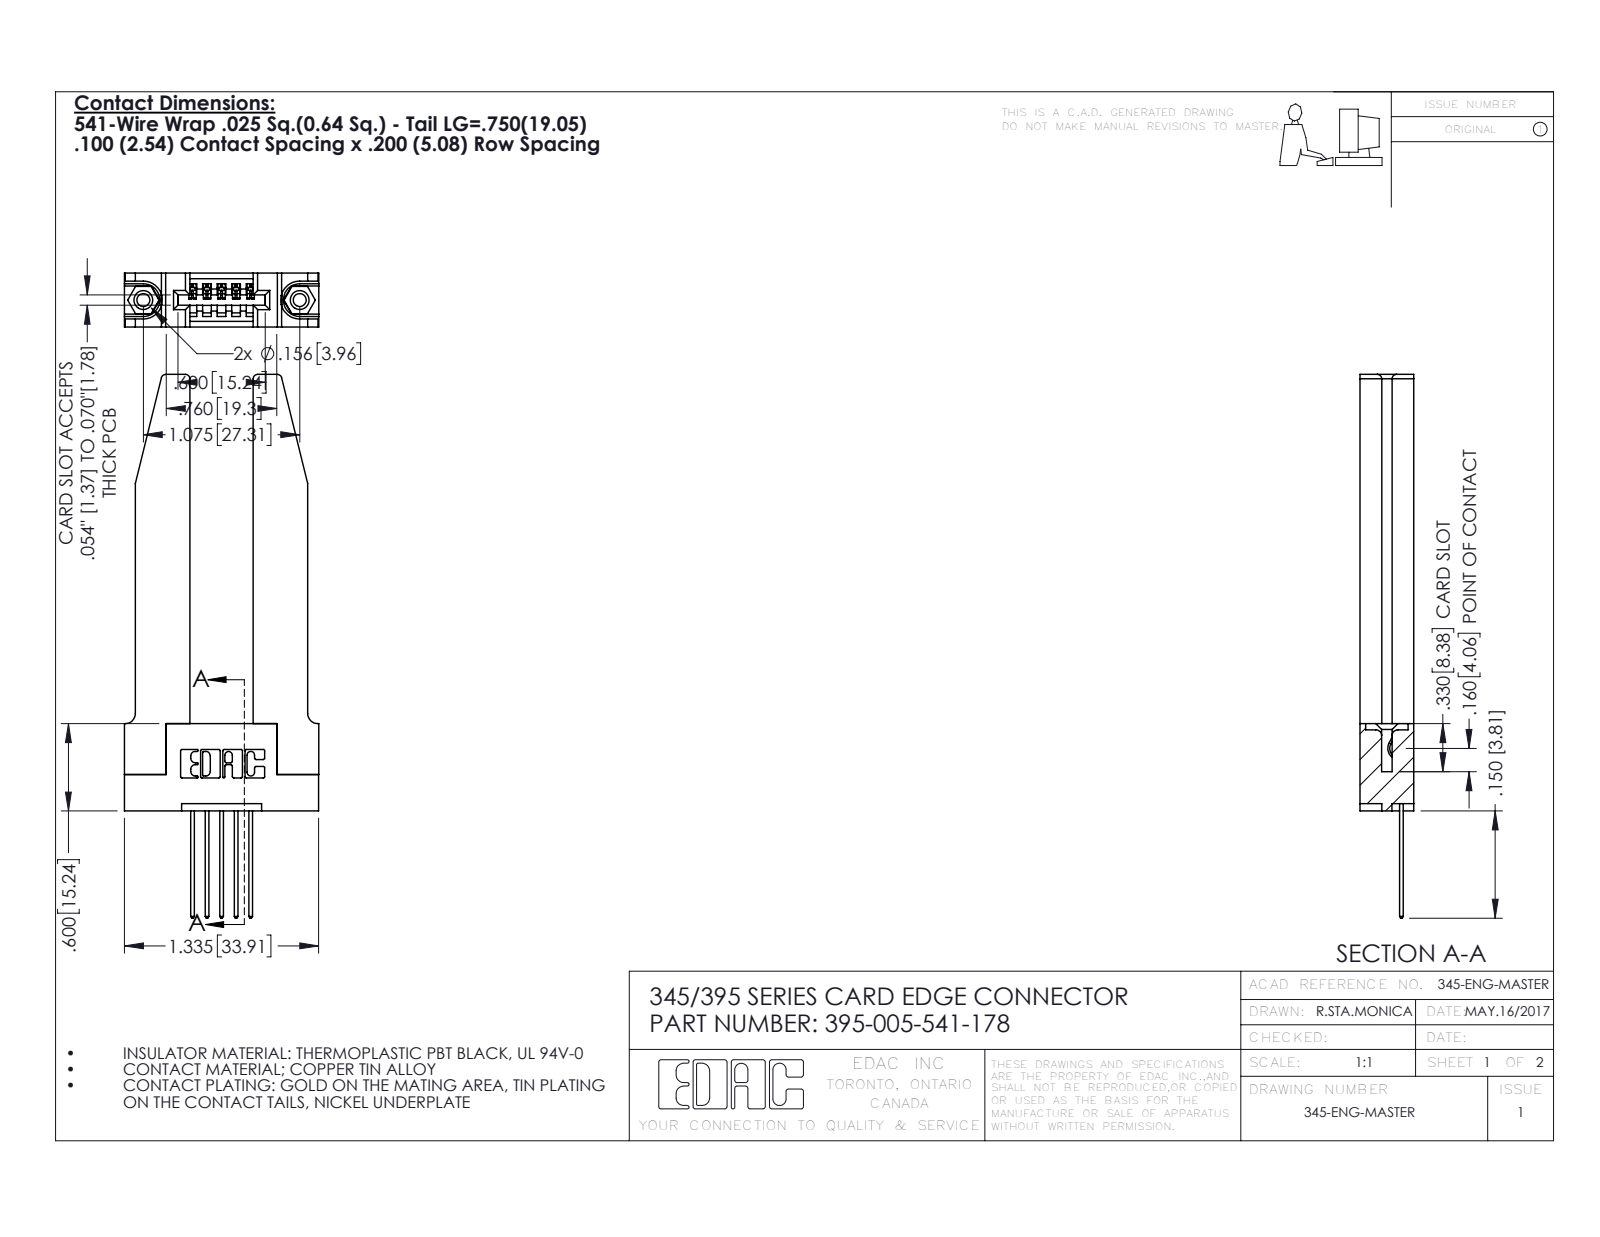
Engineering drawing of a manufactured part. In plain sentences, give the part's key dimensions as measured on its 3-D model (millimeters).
The part is named "345 Part_Flush Mounting Lugs - 0.156 Dia-TH; 345-220-078_345-220-078; 345-292-001_345-293-141; 395-005-541-178 (+1 more)". Its 3-D file was written by "SolidWorks 2016 (CONFIG_CONTROL_DESIGN)". It is 10 solids with 650 faces: 422 planar, 176 cylindrical and 52 other. Overall it measures 94.9 by 33.9 by 9.4 millimeters. Its volume is 10 700 cubic millimeters and its surface area 10 340 square millimeters. Round holes: 2 of diameter 2.3, 2 of diameter 3.2, 2 of diameter 4, 1 of diameter 1.6. Round bosses or shafts: 2 of diameter 3.9. Partial cylindrical surfaces (rounded edges, fillets, slot ends): 22 of radius 0.3, 10 of radius 0.2, 10 of radius 0.3, 8 of radius 0.8, 6 of radius 0.2, 6 of radius 0.8, 3 of radius 0.7, 2 of radius 0.8. The main face-to-face distances are 9.4, 3.8, 5.6, 11, 3.8, 1.8, 2, 5.1, 7.6, 2.4. The hole center spacings are 6.9, 21.5, 27.3.
